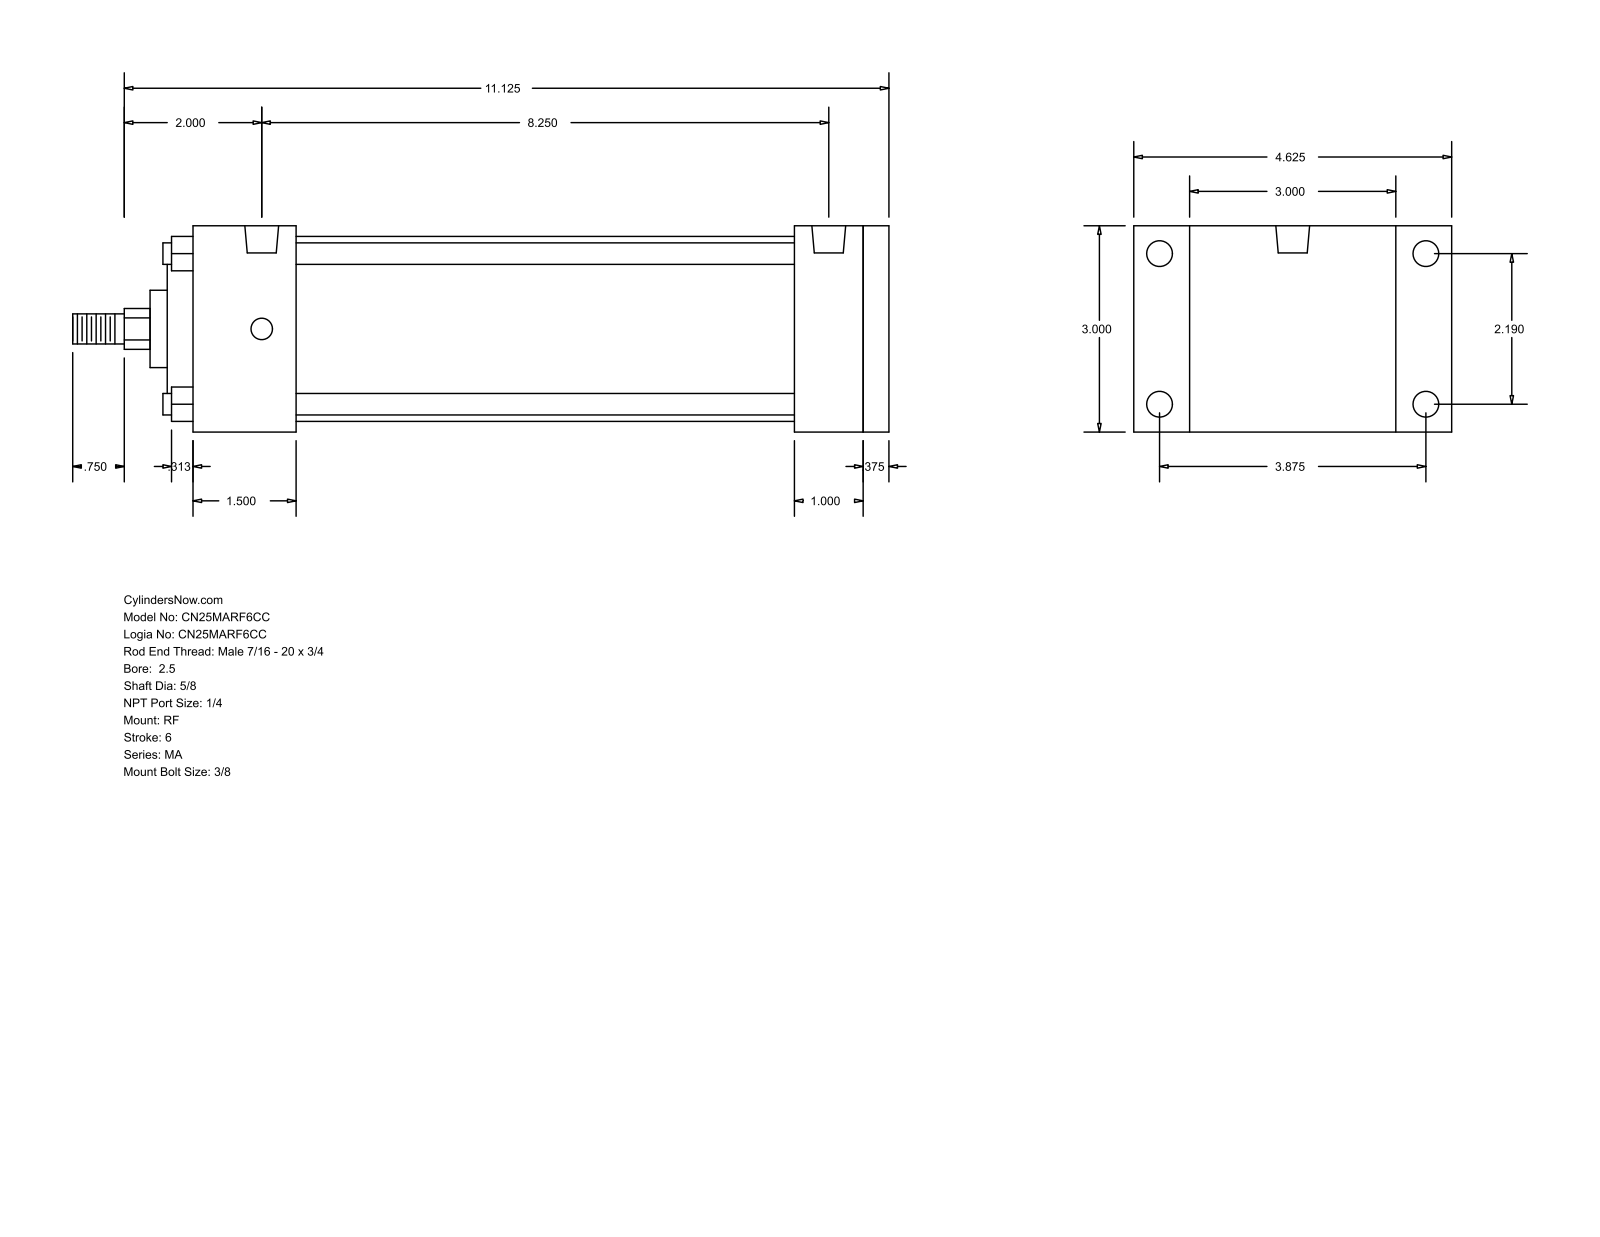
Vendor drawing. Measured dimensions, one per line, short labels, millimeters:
name: MA_RF__0250_0.625
written by: GSSL Pune (CONFIG_CONTROL_DESIGN)
unit: mm
bodies: 0 solids, 94 faces (65 planar, 29 cylindrical, 0 other)
size: 301.62 × 117.47 × 76.2
holes: 4× ⌀7.94, 4× ⌀9.53, 2× ⌀12.49
bosses: 4× ⌀7.94, 1× ⌀68.33, 1× ⌀50.8, 1× ⌀28.57, 1× ⌀15.88, 1× ⌀11.11
rounds: 1× R7.54
face distances: 76.2, 257.17, 9.52, 247.65, 25.4, 38.1, 222.25, 184.15, 209.55, 219.07
hole spacings: 55.62, 98.42, 113.05, 209.55
